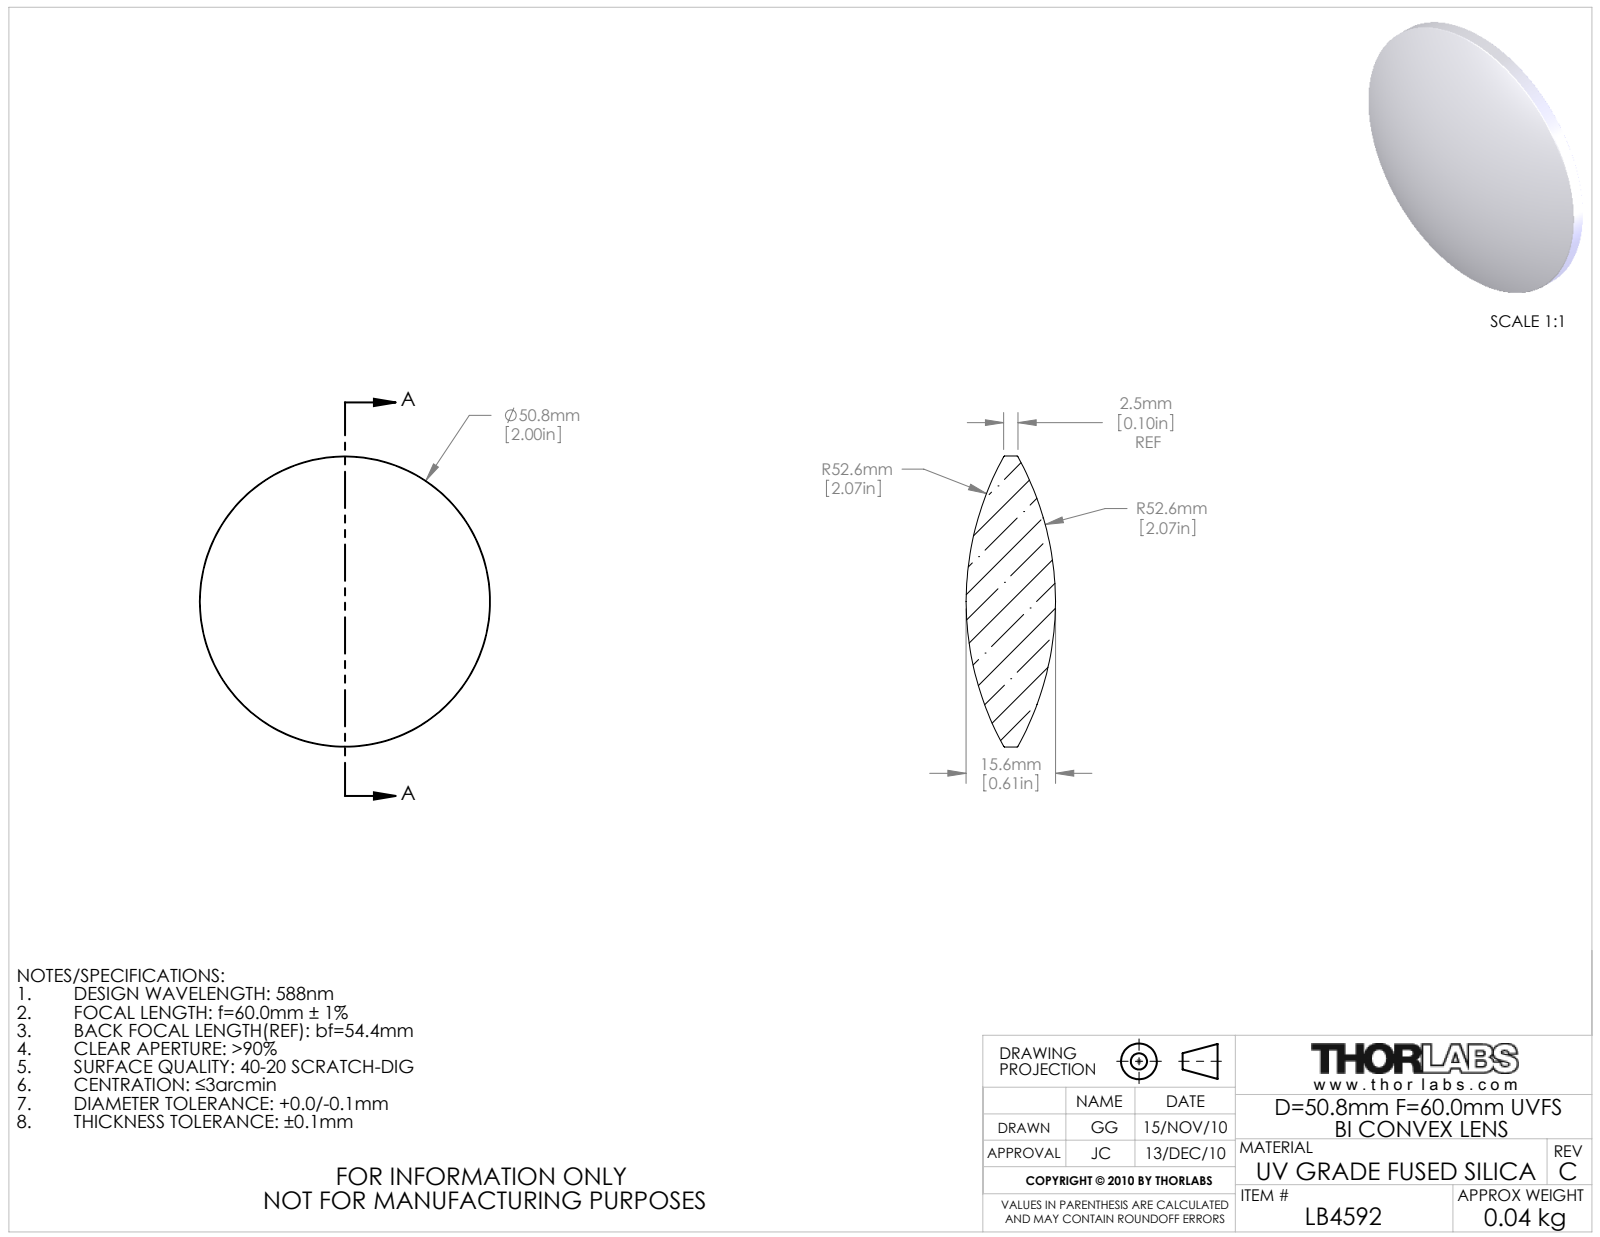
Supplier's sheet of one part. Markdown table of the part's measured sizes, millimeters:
| quantity | value |
| --- | --- |
| part name | 3413-E0W |
| STEP written by | SolidWorks 2009 (AUTOMOTIVE_DESIGN) |
| units | millimeters |
| bodies | 1 solid, 10 faces (0 planar, 2 cylindrical, 8 other) |
| overall size | 50.8 × 50.8 × 15.6 |
| volume | 18 428 mm³ |
| surface area | 4 693 mm² |
| round bosses / shafts (diameter × count) | 50.8 × 1 |
